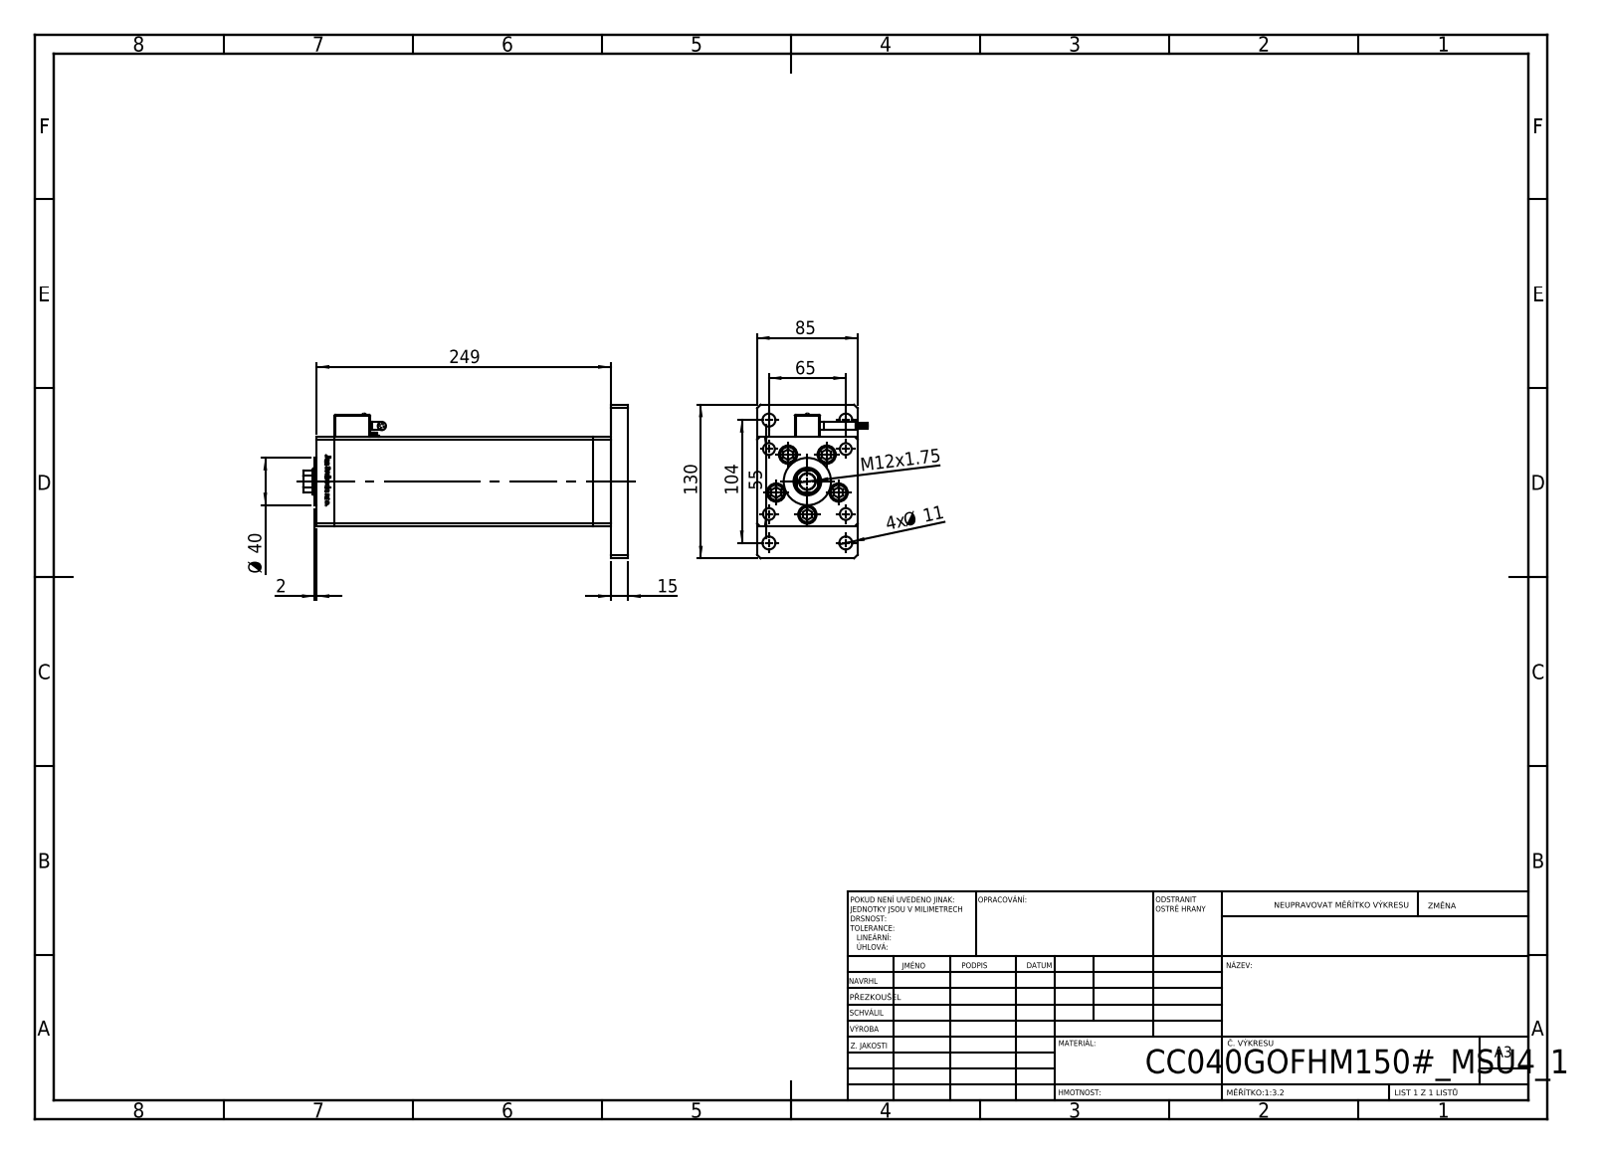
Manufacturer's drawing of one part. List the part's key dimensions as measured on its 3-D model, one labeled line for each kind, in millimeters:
Part name (STEP PRODUCT): V220C_G_MIDDLE; ALLEN BOLT; V220C_VC_G; V220C BACK_G (+3 more)
STEP written by: SolidWorks 2019 (CONFIG_CONTROL_DESIGN)
Units: millimetres
Bodies: 19 solids, 577 faces (247 planar, 190 cylindrical, 140 other)
Overall size (bounding box): 275 × 130 × 93.3
Volume: 1 463 000 mm³ · Surface area: 214 016 mm²
Round holes (diameter × count): ⌀10 ×9, ⌀11 ×9, ⌀15.5 ×5, ⌀14.5 ×4, ⌀3.6 ×1, ⌀5 ×1, ⌀7 ×1, ⌀13.5 ×1, ⌀22 ×1, ⌀56 ×1
Round bosses / shafts (diameter × count): ⌀8 ×9, ⌀14.5 ×5, ⌀0.85 ×4, ⌀7 ×2, ⌀40 ×1, ⌀6 ×1, ⌀3.5 ×1, ⌀2.5 ×1
Partial cylindrical surfaces — rounded edges, fillets, slot ends (radius × count): R1 ×14, R0.93 ×2, R4 ×2, R10.5 ×1
Main face-to-face distances: 15, 85, 75, 30, 218.5, 248.5, 233.5, 2, 13, 68.5
Hole centre spacings: 28, 24.5, 42.57, 61.32, 65, 69.46, 79.5, 102.69
